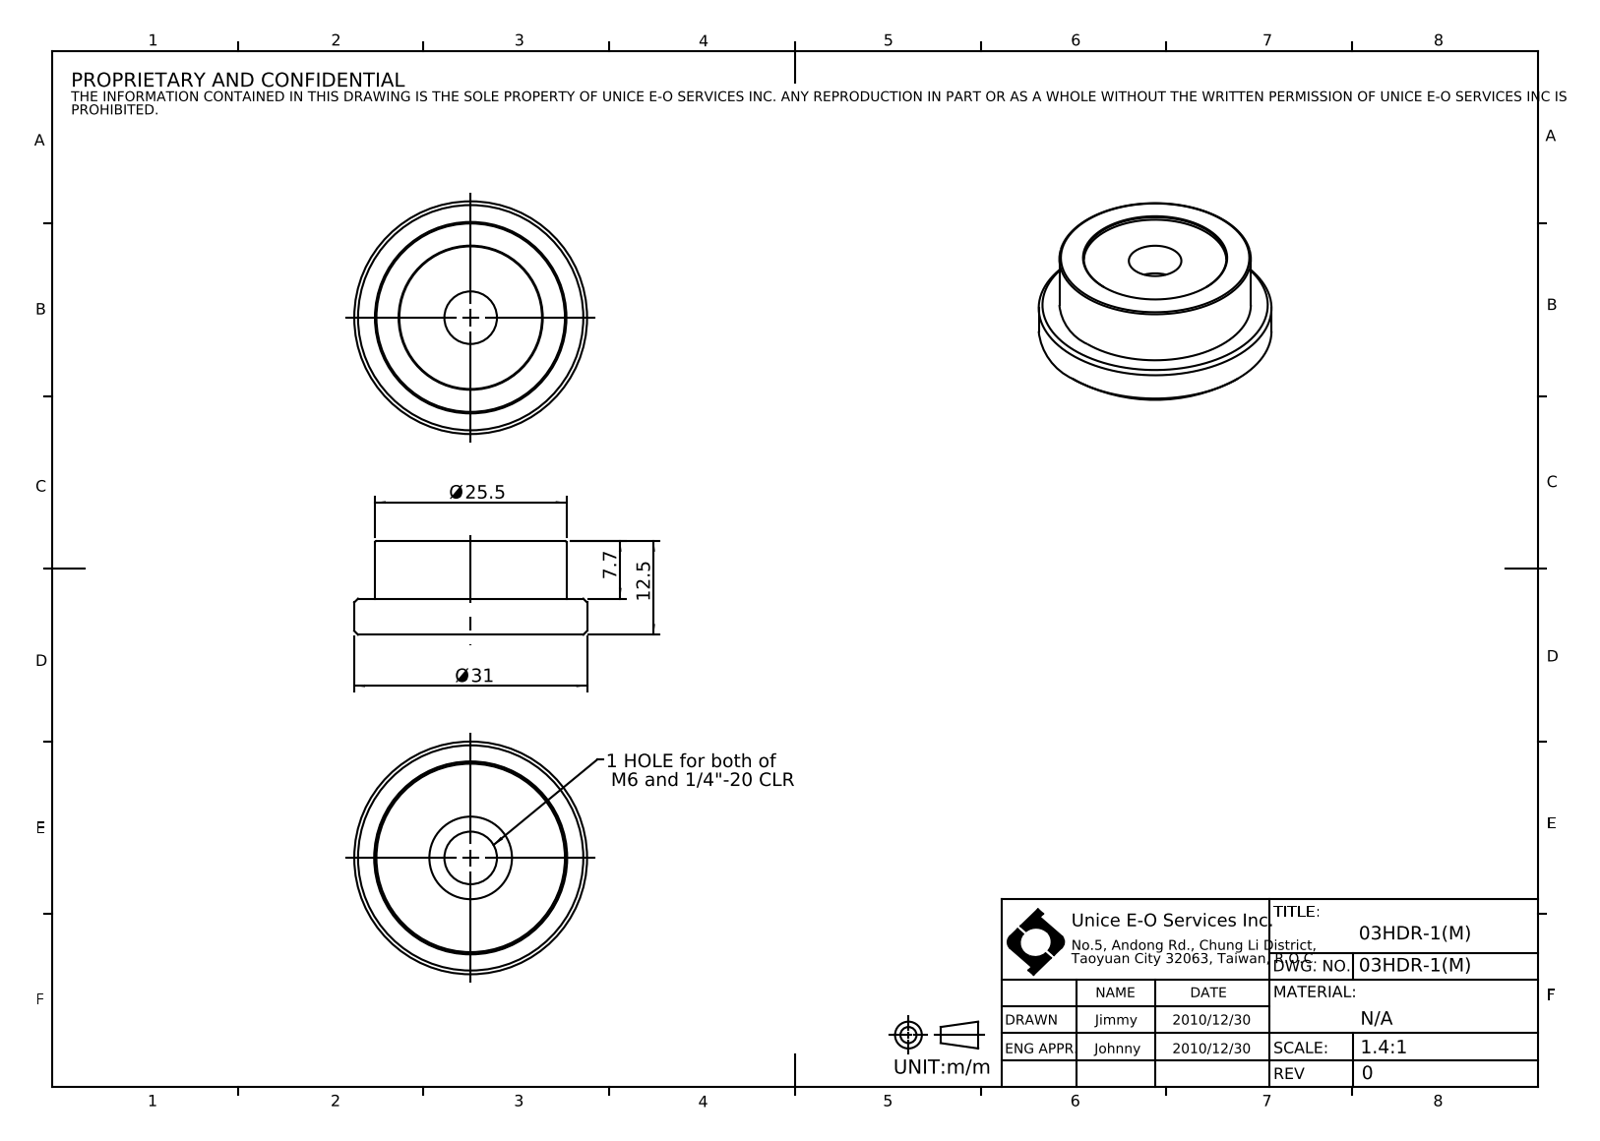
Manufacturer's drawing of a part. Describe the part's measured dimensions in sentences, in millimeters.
The part is named "03HDR-1(M)". Its 3-D file was written by "SolidWorks 2016 (CONFIG_CONTROL_DESIGN)". It is 1 solid with 30 faces: 6 planar, 12 cylindrical and 12 other. Overall it measures 31 by 31 by 12.5 millimeters. Its volume is 6 295 cubic millimeters and its surface area 2 848 square millimeters. Round holes: 1 of diameter 7, 1 of diameter 11, 1 of diameter 19, 1 of diameter 25.5. Round bosses or shafts: 1 of diameter 31. The main face-to-face distances are 0.5, 12, 11.5, 4.3, 7.2, 7.7, 4.8, 12.5, 7.5, 7.
